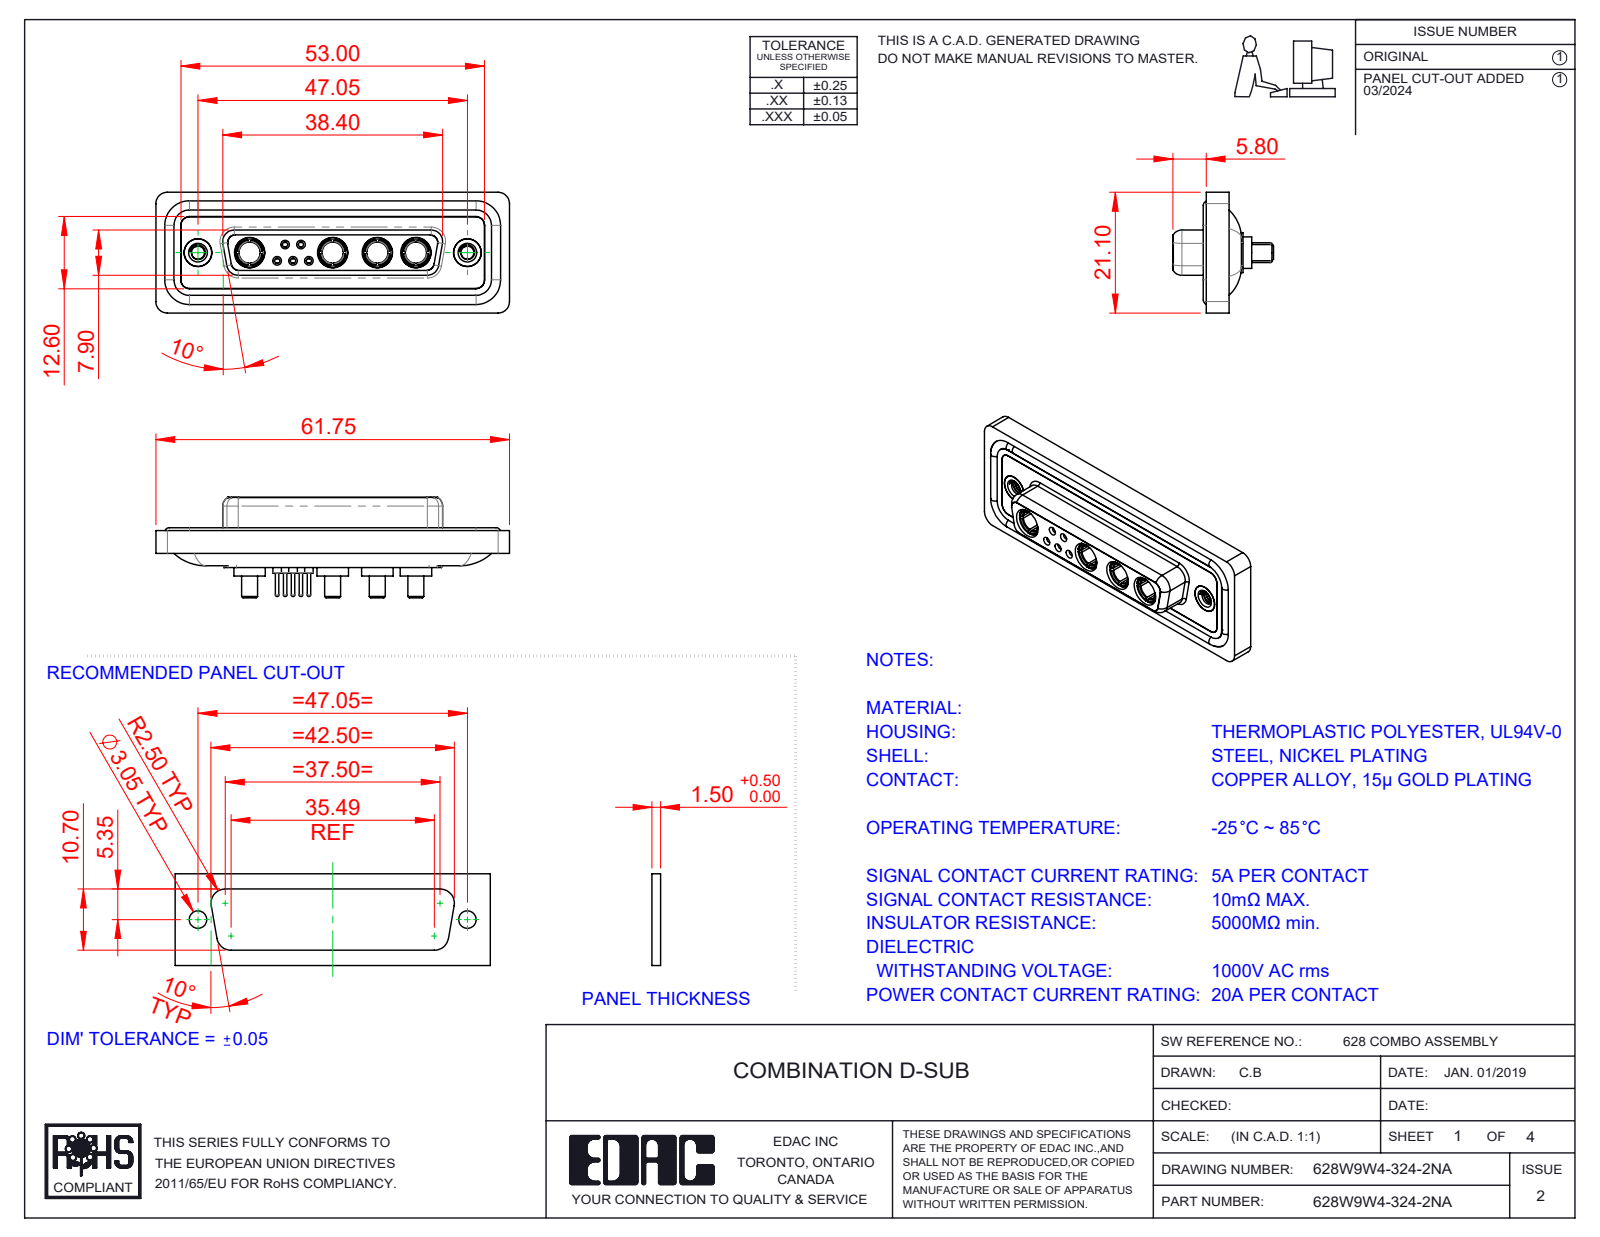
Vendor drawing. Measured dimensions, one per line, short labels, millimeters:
name: 628Combo Contact Row 2_24; 628Combo Waterproof Housing_25 Contacts; 628Combo Shell Front_25 Contacts; Power Socket_20A S (+5 more)
written by: SolidWorks 2023 (CONFIG_CONTROL_DESIGN)
unit: mm
bodies: 20 solids, 955 faces (296 planar, 377 cylindrical, 282 other)
size: 61.75 × 21.1 × 17.55
volume: 8 225 mm³; area: 13 559 mm²
holes: 6× ⌀4.85, 5× ⌀0.9, 5× ⌀1.1, 5× ⌀1.5, 5× ⌀2, 4× ⌀3.7, 4× ⌀5.3, 3× ⌀1.6, 2× ⌀1.7, 2× ⌀2.26, 2× ⌀4, 2× ⌀4.05
bosses: 6× ⌀1.6, 5× ⌀2.2, 5× ⌀0.6, 4× ⌀5.5, 4× ⌀5.2, 4× ⌀4.96, 4× ⌀4.75, 4× ⌀3.75
rounds: 22× R1.5, 18× R2, 8× R1.35, 8× R1.6, 4× R0.25, 4× R0.5, 4× R0.6, 4× R0.65
face distances: 0.4, 1.8, 7.45, 5.65, 0.5, 7.05, 6.6, 1.6, 1.1, 2.9
hole spacings: 3.16, 2.77, 5.03, 2.76, 4.4, 5.02, 5.54, 5.73
